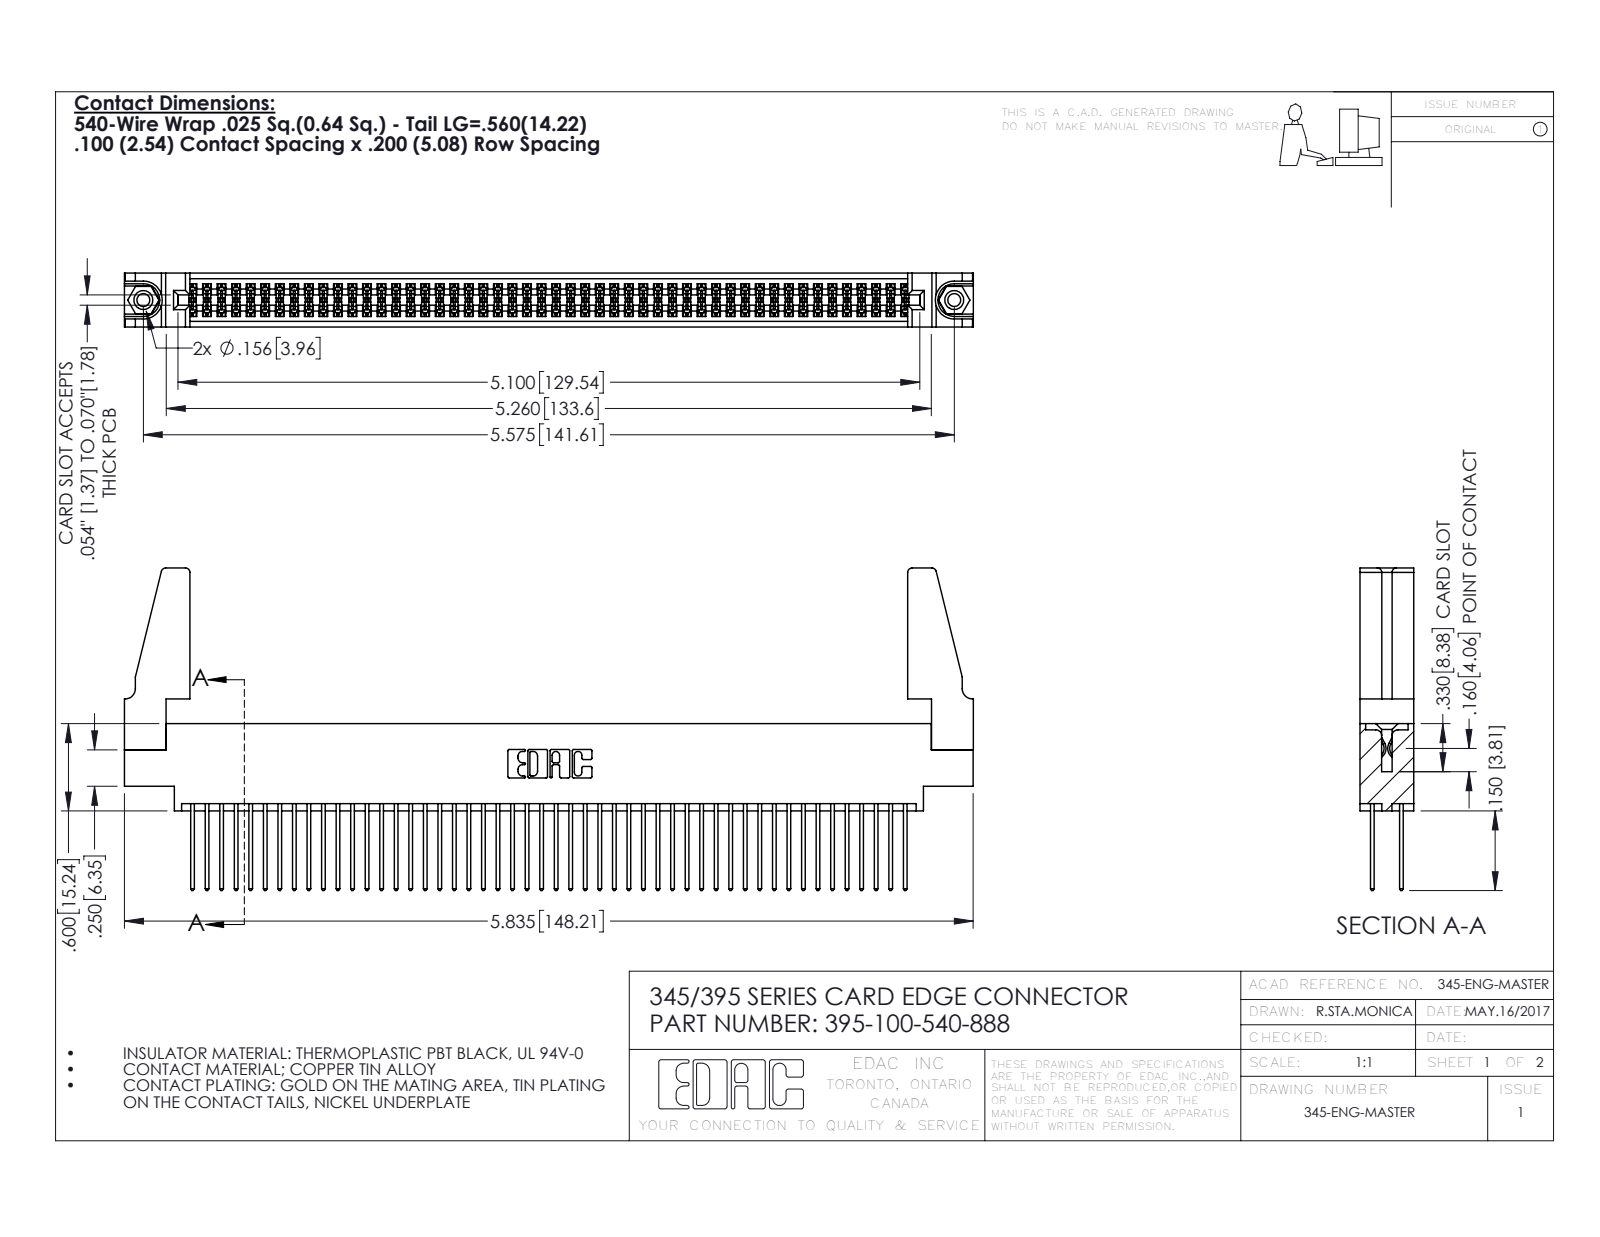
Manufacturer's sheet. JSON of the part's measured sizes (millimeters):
{"part_name": "395-100-540-888; 345-292-001_345-293-140; 345 Part_0.170 Offset - 0.156 Dia-TH; 345-220-078_345-220-088 (+1 more)", "step_written_by": "SolidWorks 2016 (CONFIG_CONTROL_DESIGN)", "units": "millimeters", "bodies": {"solids": 105, "faces": 5254, "planar": 3456, "cylindrical": 1782, "other": 16}, "overall_size": [148.2, 56.3, 9.4], "volume_mm3": 17990, "surface_area_mm2": 26970, "round_holes": [[2.3, 2], [3.2, 2], [4, 2], [1.6, 1]], "round_bosses_or_shafts": [[3.9, 2]], "partial_cylinders_radius": [[0.2, 150], [0.3, 100], [0.3, 22], [0.8, 8], [0.2, 6], [0.8, 6], [0.7, 3], [0.4, 2]], "face_to_face_distances": [1.8, 7.6, 9.4, 2.5, 6.9, 0.6, 5.1, 5.7, 4.4, 3.8], "hole_center_spacings": [6.9, 135.6, 141.6]}
